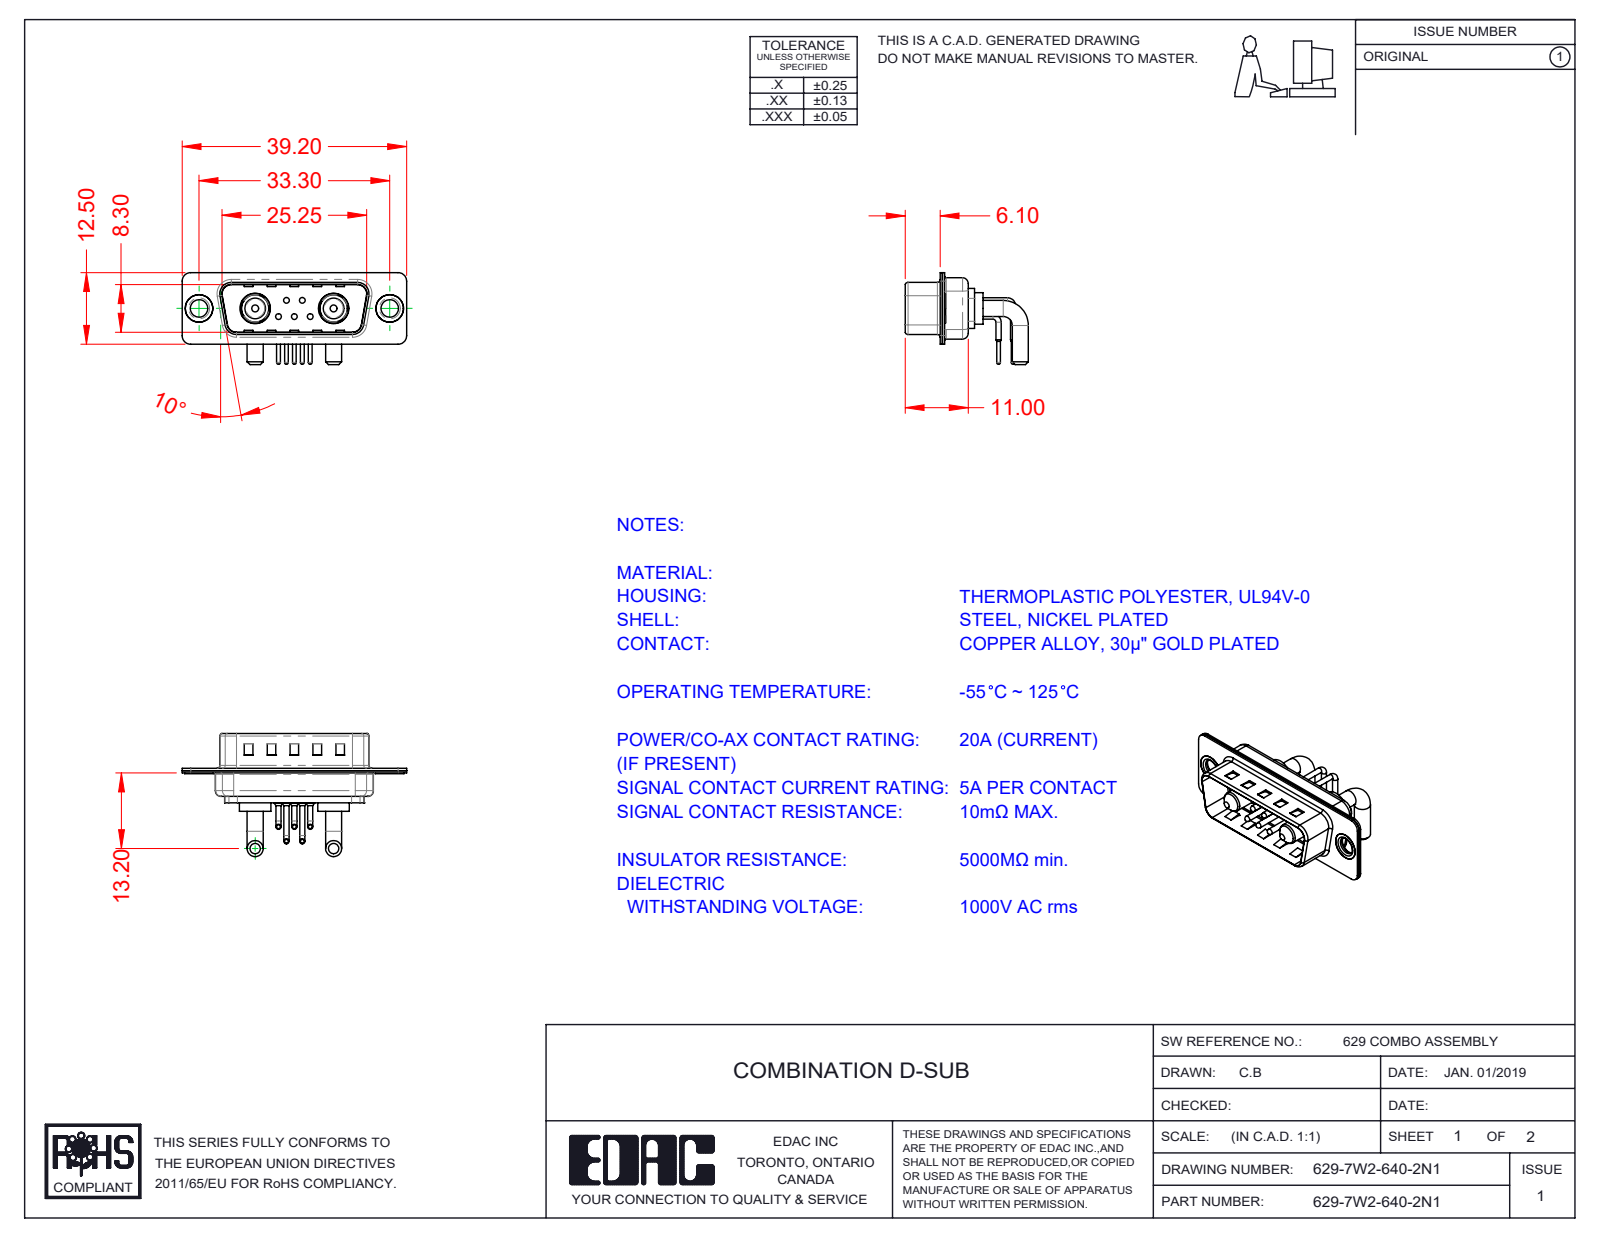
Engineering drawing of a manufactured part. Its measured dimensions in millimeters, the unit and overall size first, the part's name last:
Units: millimetres
Overall size (bounding box): 39.2 × 21.5 × 16.05
Round holes (diameter × count): ⌀0.75 ×5, ⌀1.6 ×5, ⌀2 ×5, ⌀3.05 ×2, ⌀4 ×2, ⌀4.8 ×2, ⌀4.85 ×2, ⌀5.3 ×2
Round bosses / shafts (diameter × count): ⌀0.9 ×10, ⌀1.5 ×5, ⌀1 ×5, ⌀0.65 ×5, ⌀2.8 ×4, ⌀5.5 ×2, ⌀5.2 ×2, ⌀5 ×2
Partial cylindrical surfaces — rounded edges, fillets, slot ends (radius × count): R1.5 ×16, R2 ×12, R0.5 ×8, R1.6 ×8, R1.01 ×5, R0.25 ×4, R0.6 ×4, R0.65 ×4
Main face-to-face distances: 0.4, 0.8, 9.5, 9.1, 8.7, 9.9, 0.75, 1.2, 5.6, 0.35
Hole centre spacings: 3.16, 2.77, 9.8, 23.5, 4.31, 4.33, 5.03, 5.04
Volume: 2 077 mm³ · Surface area: 4 949 mm²
Bodies: 14 solids, 950 faces (479 planar, 339 cylindrical, 132 other)
Part name (STEP PRODUCT): 629-7W2-640-2N1; 629Combo Shell Rear_15 Contacts; 629Combo Thru Hole Rivet; 629Combo Contact Row 2 (+4 more)
STEP written by: SolidWorks 2020 (CONFIG_CONTROL_DESIGN)
